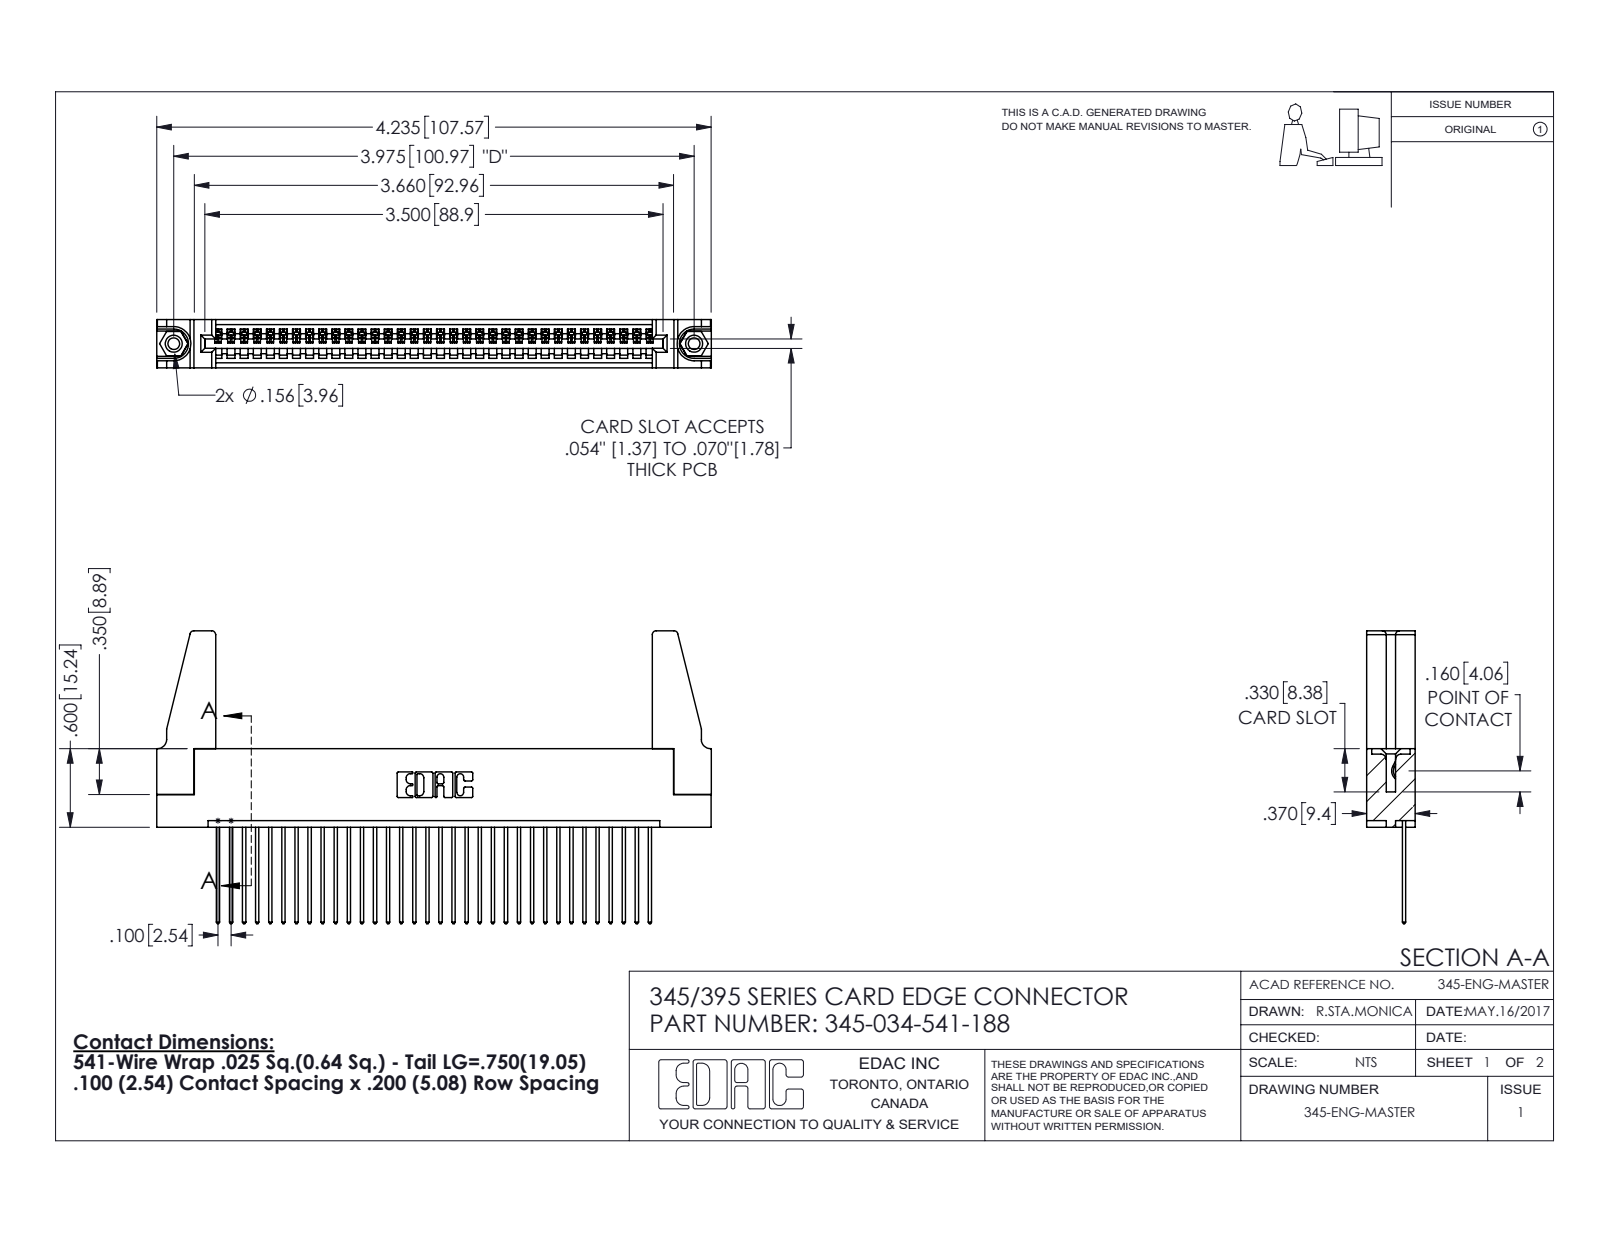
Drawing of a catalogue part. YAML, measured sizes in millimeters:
part_name: "345-034-541-188; 345-220-078_345-220-088; 345-250-001_345-250-001-102; 345-292-001_345-293-141 (+1 more)"
step_written_by: "SolidWorks 2016 (CONFIG_CONTROL_DESIGN)"
units: millimeters
bodies: {solids: 39, faces: 2222, planar: 1512, cylindrical: 694, other: 16}
overall_size: [107.6, 56.8, 9.4]
volume: 13500
surface_area: 17320
round_holes:
  - {diameter: 2.3, count: 2}
  - {diameter: 3.2, count: 2}
  - {diameter: 4, count: 2}
  - {diameter: 1.6, count: 1}
round_bosses_or_shafts:
  - {diameter: 3.9, count: 2}
partial_cylinders:
  - {radius: 0.2, count: 68}
  - {radius: 0.3, count: 68}
  - {radius: 0.3, count: 22}
  - {radius: 0.8, count: 8}
  - {radius: 0.2, count: 6}
  - {radius: 0.8, count: 6}
  - {radius: 0.7, count: 3}
  - {radius: 0.8, count: 2}
face_to_face_distances: [1.8, 7.6, 9.4, 5.1, 2.5, 6.9, 0.6, 5.7, 3.8, 1.8]
hole_center_spacings: [6.9, 95, 101]
